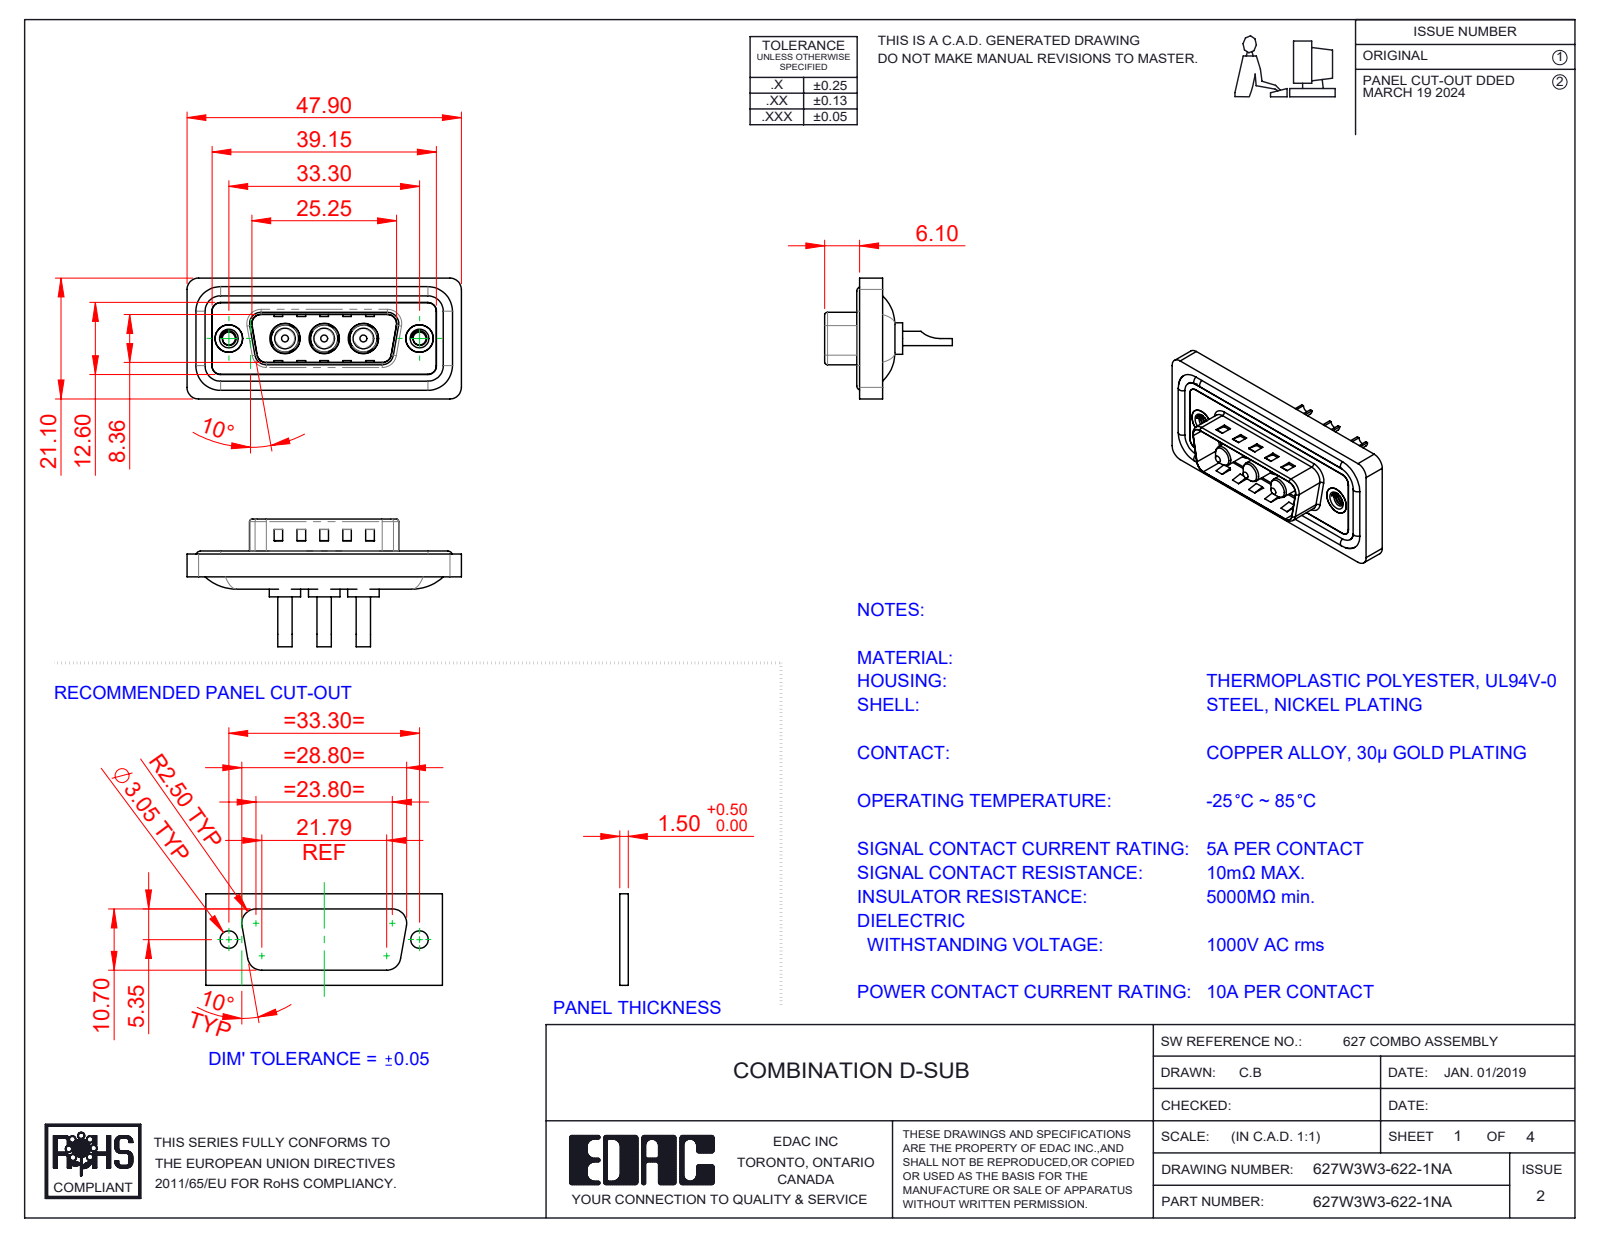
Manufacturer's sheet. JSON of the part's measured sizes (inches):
{"part_name": "627Combo Waterproof Housing_15 Contacts; 627Combo Shell Rear_15 Contacts; 627Combo Threaded Rivet_A; 627Combo Housing_3W3 (+3 more)", "step_written_by": "SolidWorks 2023 (CONFIG_CONTROL_DESIGN)", "units": "inches", "bodies": {"solids": 13, "faces": 580, "planar": 213, "cylindrical": 252, "other": 115}, "overall_size": [1.886, 0.878, 0.831], "volume_in3": 0.34, "surface_area_in2": 13.79, "round_holes": [[0.067, 3], [0.191, 3], [0.209, 3], [0.089, 2], [0.157, 2], [0.189, 2], [0.197, 2]], "round_bosses_or_shafts": [[0.063, 4], [0.217, 3], [0.205, 3], [0.187, 3], [0.148, 3], [0.142, 3], [0.098, 3], [0.193, 2]], "partial_cylinders_radius": [[0.059, 26], [0.079, 20], [0.02, 8], [0.063, 8], [0.01, 4], [0.024, 4], [0.026, 4], [0.035, 4]], "face_to_face_distances": [0.016, 0.043, 0.059, 0.02, 0.063, 0.122, 0.114, 0.157, 0.032, 0.377], "hole_center_spacings": [0.27, 0.386, 0.656, 0.925, 0.539, 1.311]}
